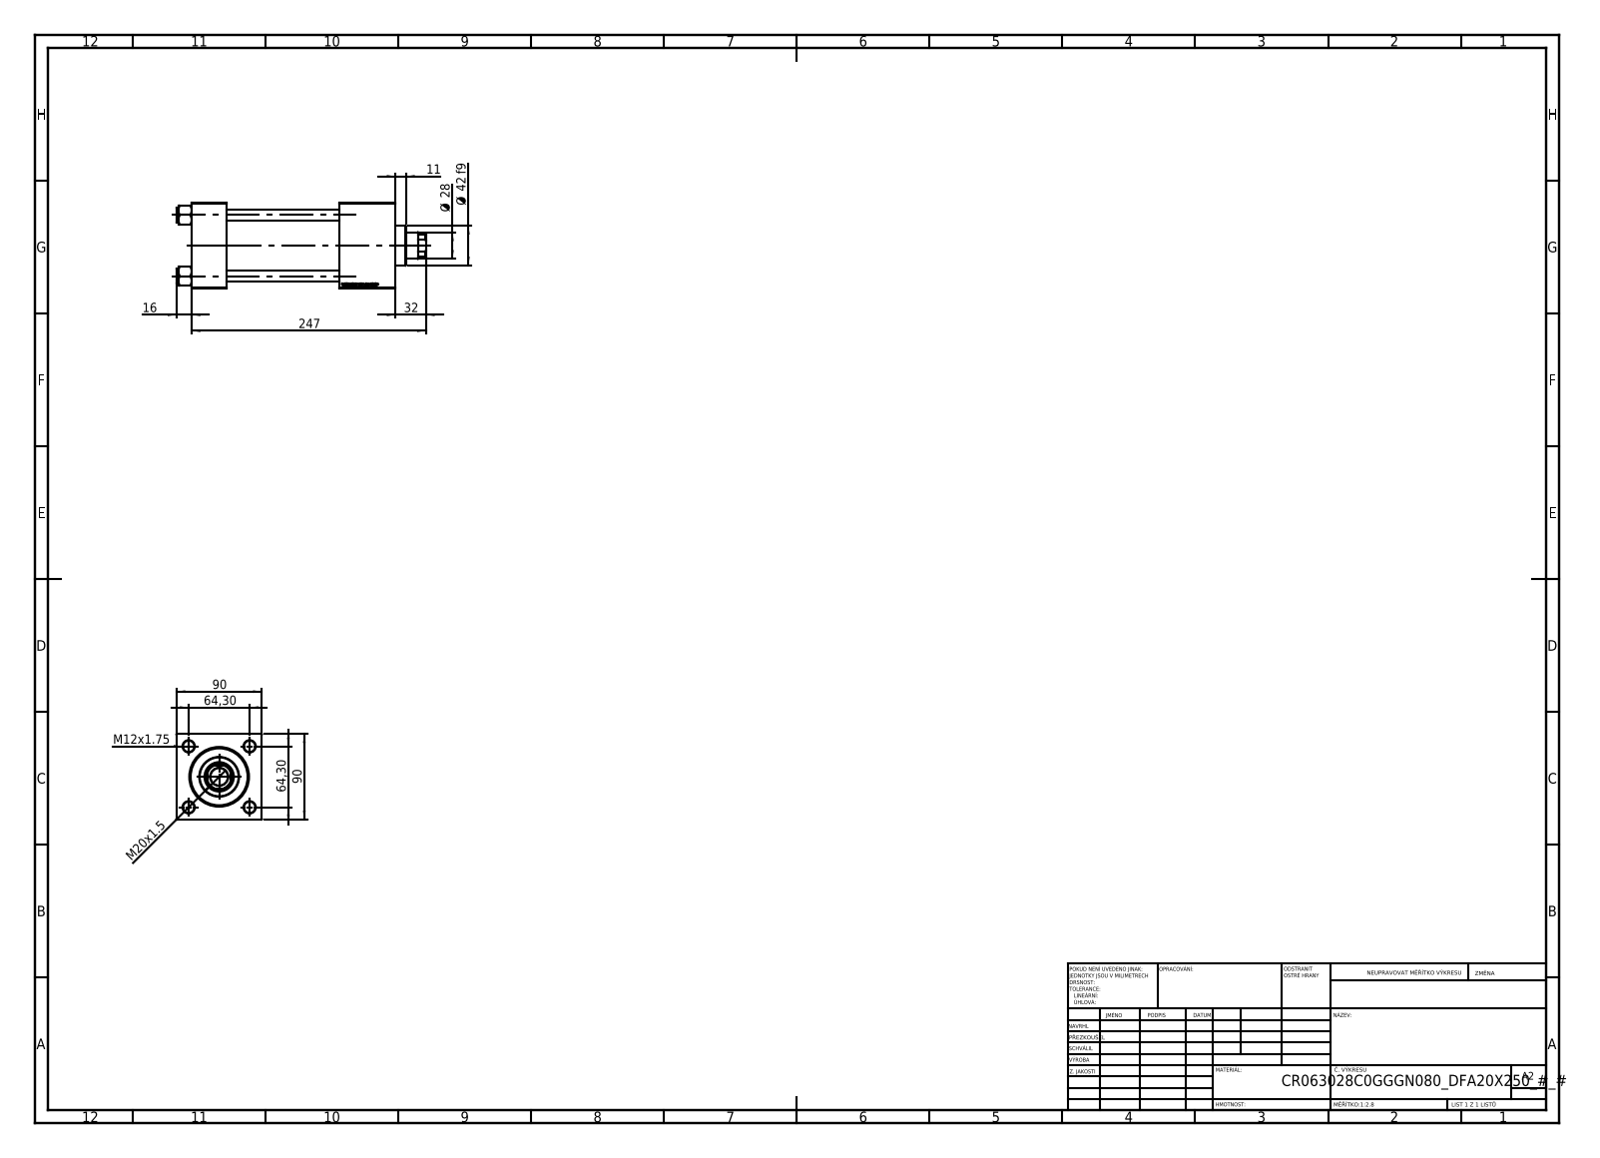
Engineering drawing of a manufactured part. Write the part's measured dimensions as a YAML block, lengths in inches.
part_name: "V215CR_VCP_C; V215_VC_A; NUT_M5_C; FEMALE_PART_FOR_DFA (+2 more)"
step_written_by: "SolidWorks 2019 (CONFIG_CONTROL_DESIGN)"
units: inches
bodies: {solids: 12, faces: 1182, planar: 538, cylindrical: 96, other: 548}
overall_size: [10.354, 3.543, 3.543]
volume: 65.42
surface_area: 350.3
round_holes:
  - {diameter: 0.472, count: 4}
  - {diameter: 0.276, count: 2}
  - {diameter: 0.825, count: 2}
  - {diameter: 1.181, count: 2}
  - {diameter: 0.728, count: 1}
  - {diameter: 1.102, count: 1}
  - {diameter: 1.22, count: 1}
  - {diameter: 1.969, count: 1}
  - {diameter: 2.362, count: 1}
  - {diameter: 2.48, count: 1}
round_bosses_or_shafts:
  - {diameter: 0.591, count: 4}
  - {diameter: 2.717, count: 1}
  - {diameter: 1.654, count: 1}
  - {diameter: 1.417, count: 1}
  - {diameter: 1.181, count: 1}
  - {diameter: 0.787, count: 1}
  - {diameter: 0.709, count: 1}
partial_cylinders:
  - {radius: 0.295, count: 1}
  - {radius: 0.472, count: 1}
  - {radius: 0.531, count: 1}
face_to_face_distances: [3.543, 1.457, 7.008, 8.465, 6.142, 4.685, 2.323, 7.335, 5.878, 1.193]
hole_center_spacings: [1.79, 2.531, 3.58, 6.201]
